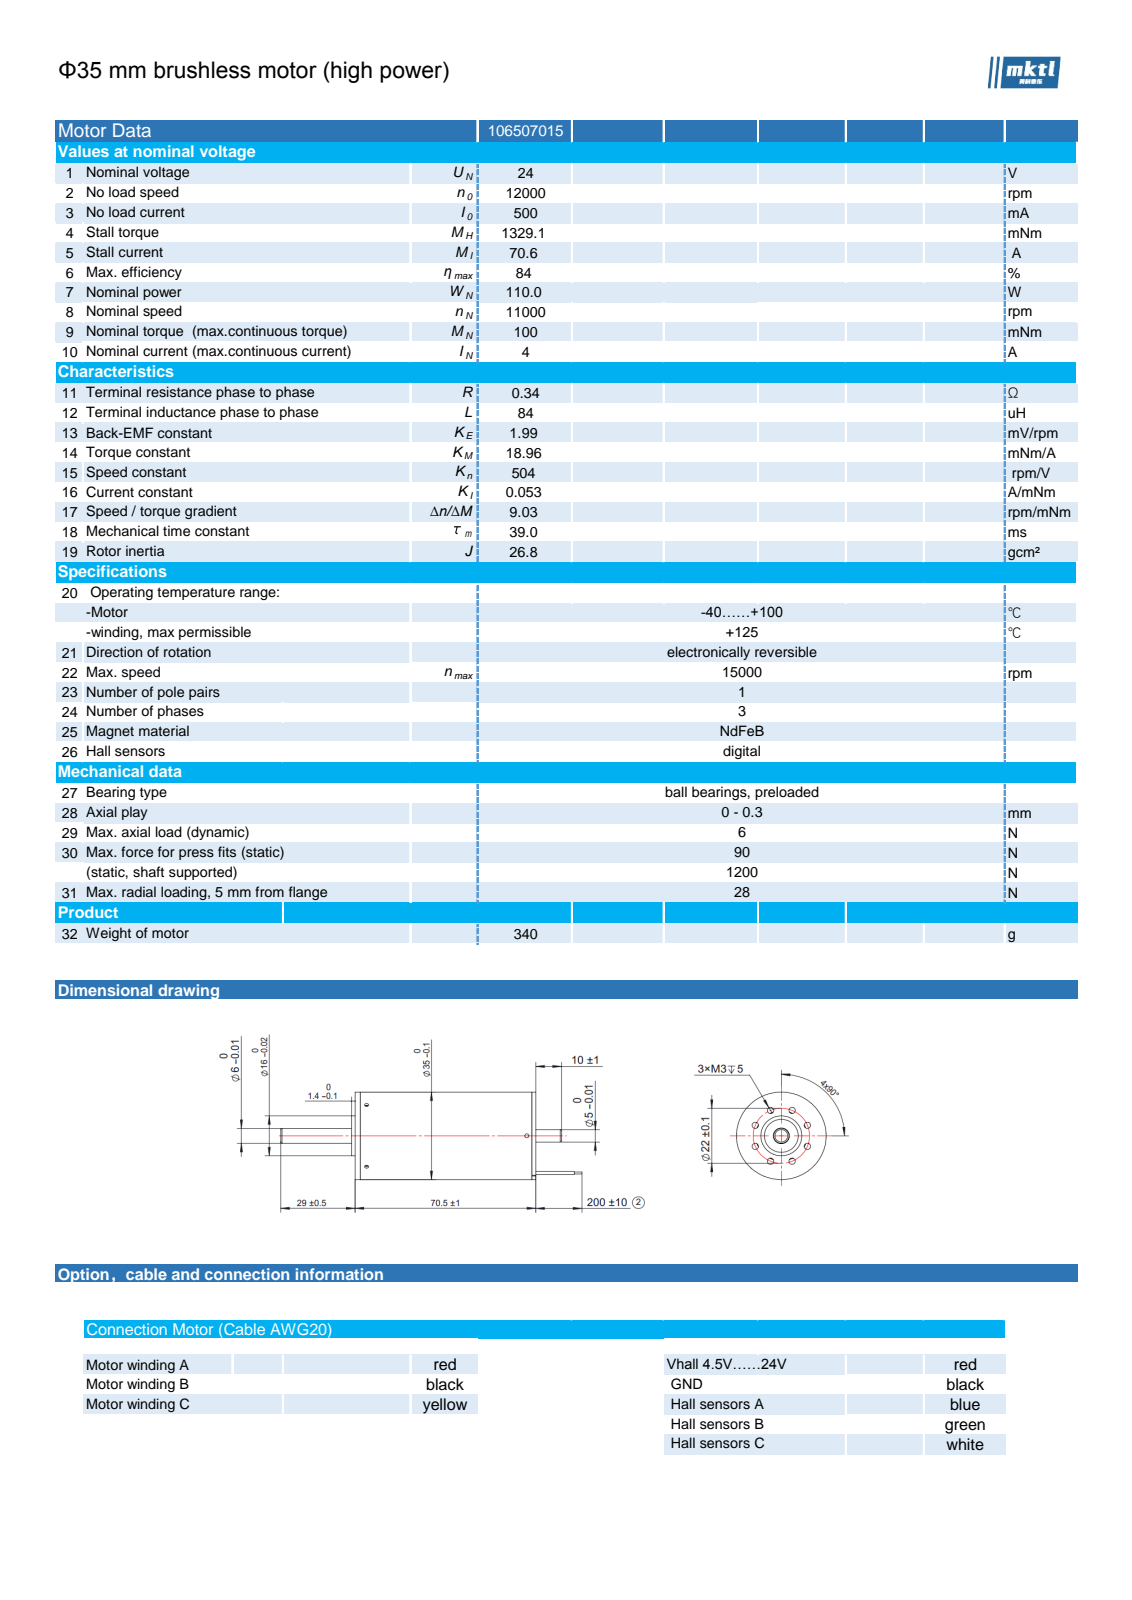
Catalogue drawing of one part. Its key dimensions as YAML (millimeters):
part_name: "106507015"
step_written_by: "SolidWorks 2025 (AUTOMOTIVE_DESIGN)"
units: millimeters
bodies: {solids: 330, faces: 3072, planar: 1325, cylindrical: 1575, other: 172}
overall_size: [117.5, 35, 35]
volume: 63385
surface_area: 265602
round_holes:
  - {diameter: 2.5, count: 8}
  - {diameter: 2.1, count: 6}
  - {diameter: 0.75, count: 5}
  - {diameter: 1, count: 4}
  - {diameter: 1.5, count: 3}
  - {diameter: 1.6, count: 3}
  - {diameter: 3, count: 3}
  - {diameter: 1.25, count: 2}
  - {diameter: 3.1, count: 2}
  - {diameter: 6, count: 1}
  - {diameter: 9.5, count: 1}
  - {diameter: 10, count: 1}
round_bosses_or_shafts:
  - {diameter: 0.58, count: 6}
  - {diameter: 1, count: 5}
  - {diameter: 0.6, count: 5}
  - {diameter: 4, count: 3}
  - {diameter: 1.6, count: 3}
  - {diameter: 1.2, count: 3}
  - {diameter: 0.8, count: 3}
  - {diameter: 3, count: 2}
partial_cylinders:
  - {radius: 0.1, count: 24}
  - {radius: 0.75, count: 11}
  - {radius: 0.42, count: 8}
  - {radius: 0.3, count: 5}
  - {radius: 1, count: 4}
  - {radius: 2, count: 4}
  - {radius: 0.5, count: 2}
  - {radius: 4.99, count: 1}
face_to_face_distances: [0.4, 0.6, 0.8, 1, 1.2, 1.4, 1.6, 1.8, 2, 2.2]
hole_center_spacings: [11, 15.55, 20.32, 13.25, 2, 8.41, 8.42, 22]
